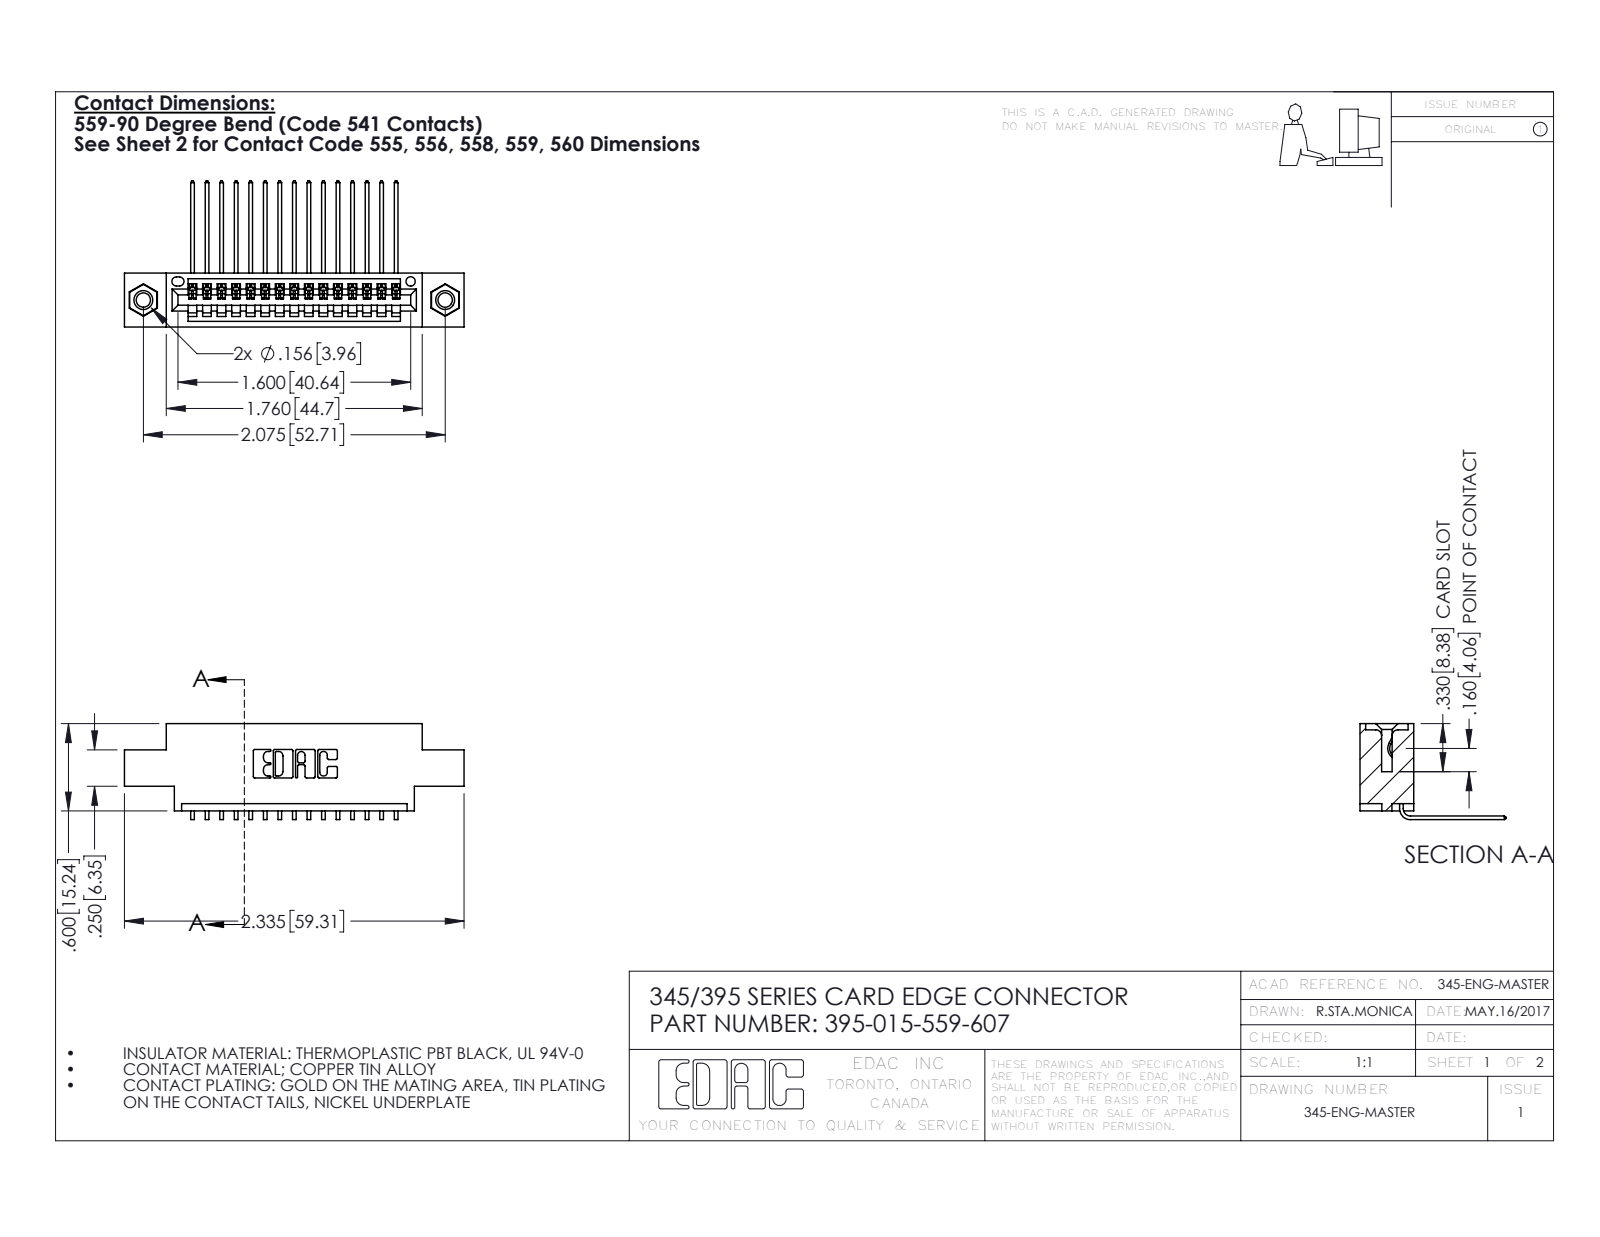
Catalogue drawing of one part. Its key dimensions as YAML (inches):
part_name: "345-250-001_345-250-005-103; 345 Part_0.170 Offset - 0.156 Dia-TI; 395-015-559-607; 345-292-001_558 559 Tail - 1"
step_written_by: "SolidWorks 2016 (CONFIG_CONTROL_DESIGN)"
units: inches
bodies: {solids: 18, faces: 1090, planar: 746, cylindrical: 328, other: 16}
overall_size: [2.335, 1.005, 0.659]
volume: 0.326
surface_area: 11.12
round_holes:
  - {diameter: 0.098, count: 2}
  - {diameter: 0.125, count: 2}
  - {diameter: 0.156, count: 2}
  - {diameter: 0.064, count: 1}
round_bosses_or_shafts:
  - {diameter: 0.155, count: 2}
partial_cylinders:
  - {radius: 0.006, count: 30}
  - {radius: 0.01, count: 22}
  - {radius: 0.007, count: 6}
  - {radius: 0.031, count: 6}
  - {radius: 0.026, count: 3}
  - {radius: 0.031, count: 2}
  - {radius: 0.04, count: 2}
  - {radius: 0.014, count: 1}
face_to_face_distances: [0.37, 0.072, 0.298, 0.2, 0.098, 0.272, 0.025, 0.1, 0.225, 0.15]
hole_center_spacings: [0.27, 1.842, 2.075]
